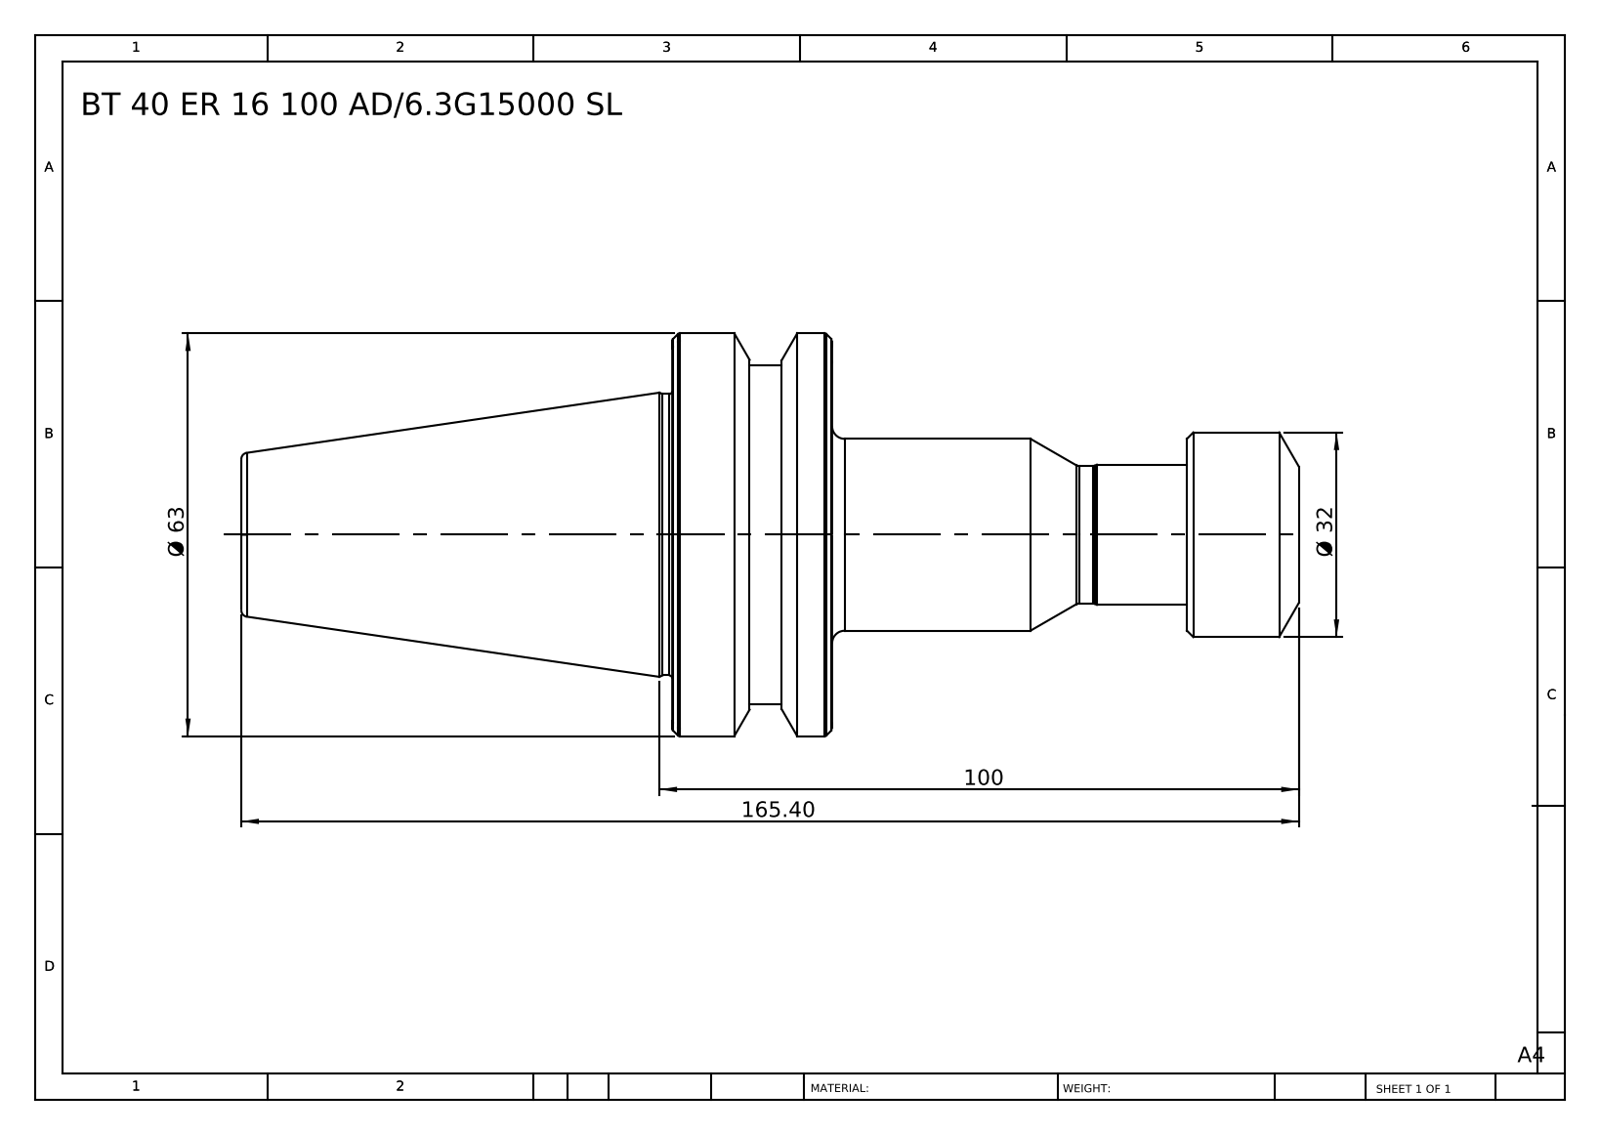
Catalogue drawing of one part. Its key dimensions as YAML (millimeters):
part_name: "BT40 ER 16 100 AD-6.3G15000 SL"
step_written_by: "SolidWorks 2014 (CONFIG_CONTROL_DESIGN)"
units: millimeters
bodies: {solids: 1, faces: 72, planar: 7, cylindrical: 16, other: 49}
overall_size: [165.4, 63, 63]
volume: 184060
surface_area: 25066
round_bosses_or_shafts:
  - {diameter: 63, count: 1}
  - {diameter: 53, count: 1}
  - {diameter: 44, count: 1}
  - {diameter: 32, count: 1}
  - {diameter: 30, count: 1}
  - {diameter: 21.9, count: 1}
  - {diameter: 21.5, count: 1}
face_to_face_distances: [25, 92.4, 67.4, 73, 98, 165.4, 17.5, 55.5, 80.5, 147.9]
